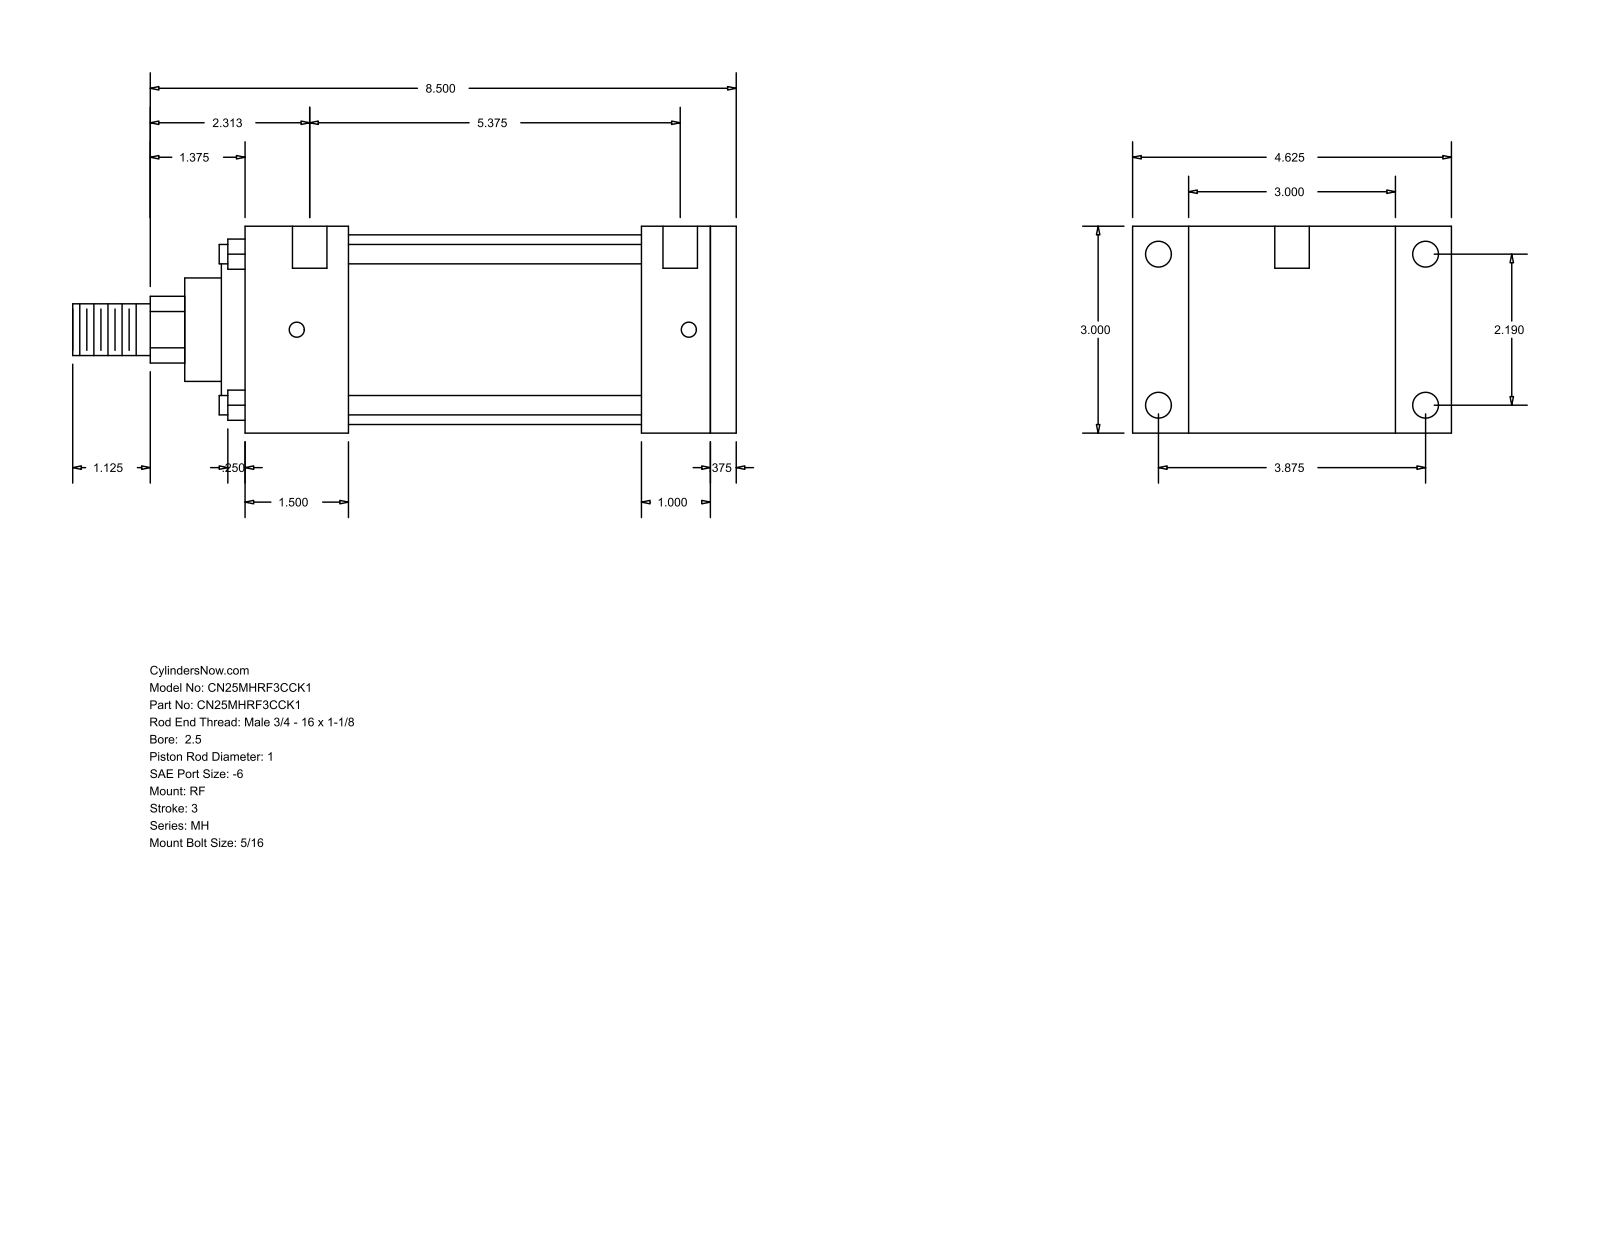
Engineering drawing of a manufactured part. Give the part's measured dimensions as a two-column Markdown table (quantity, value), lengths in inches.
| quantity | value |
| --- | --- |
| part name | MH_RF__0250_1 |
| STEP written by | GSSL Pune (CONFIG_CONTROL_DESIGN) |
| units | inches |
| bodies | 0 solids, 94 faces (65 planar, 29 cylindrical, 0 other) |
| overall size | 9.625 × 4.625 × 3 |
| round holes (diameter × count) | 0.219 × 4, 0.375 × 4, 0.5 × 2 |
| round bosses / shafts (diameter × count) | 0.281 × 4, 2.75 × 1, 2.375 × 1, 1.5 × 1, 1 × 1, 0.75 × 1 |
| partial cylindrical surfaces (radius × count) | 0.484 × 1 |
| main face-to-face distances | 3, 0.375, 7.125, 6.75, 5.75, 1, 1.375, 1.5, 4.25, 5.25 |
| hole center spacings | 2.19, 3.875, 4.451, 5.687, 0.125, 0.187, 5.375, 5.5 |
